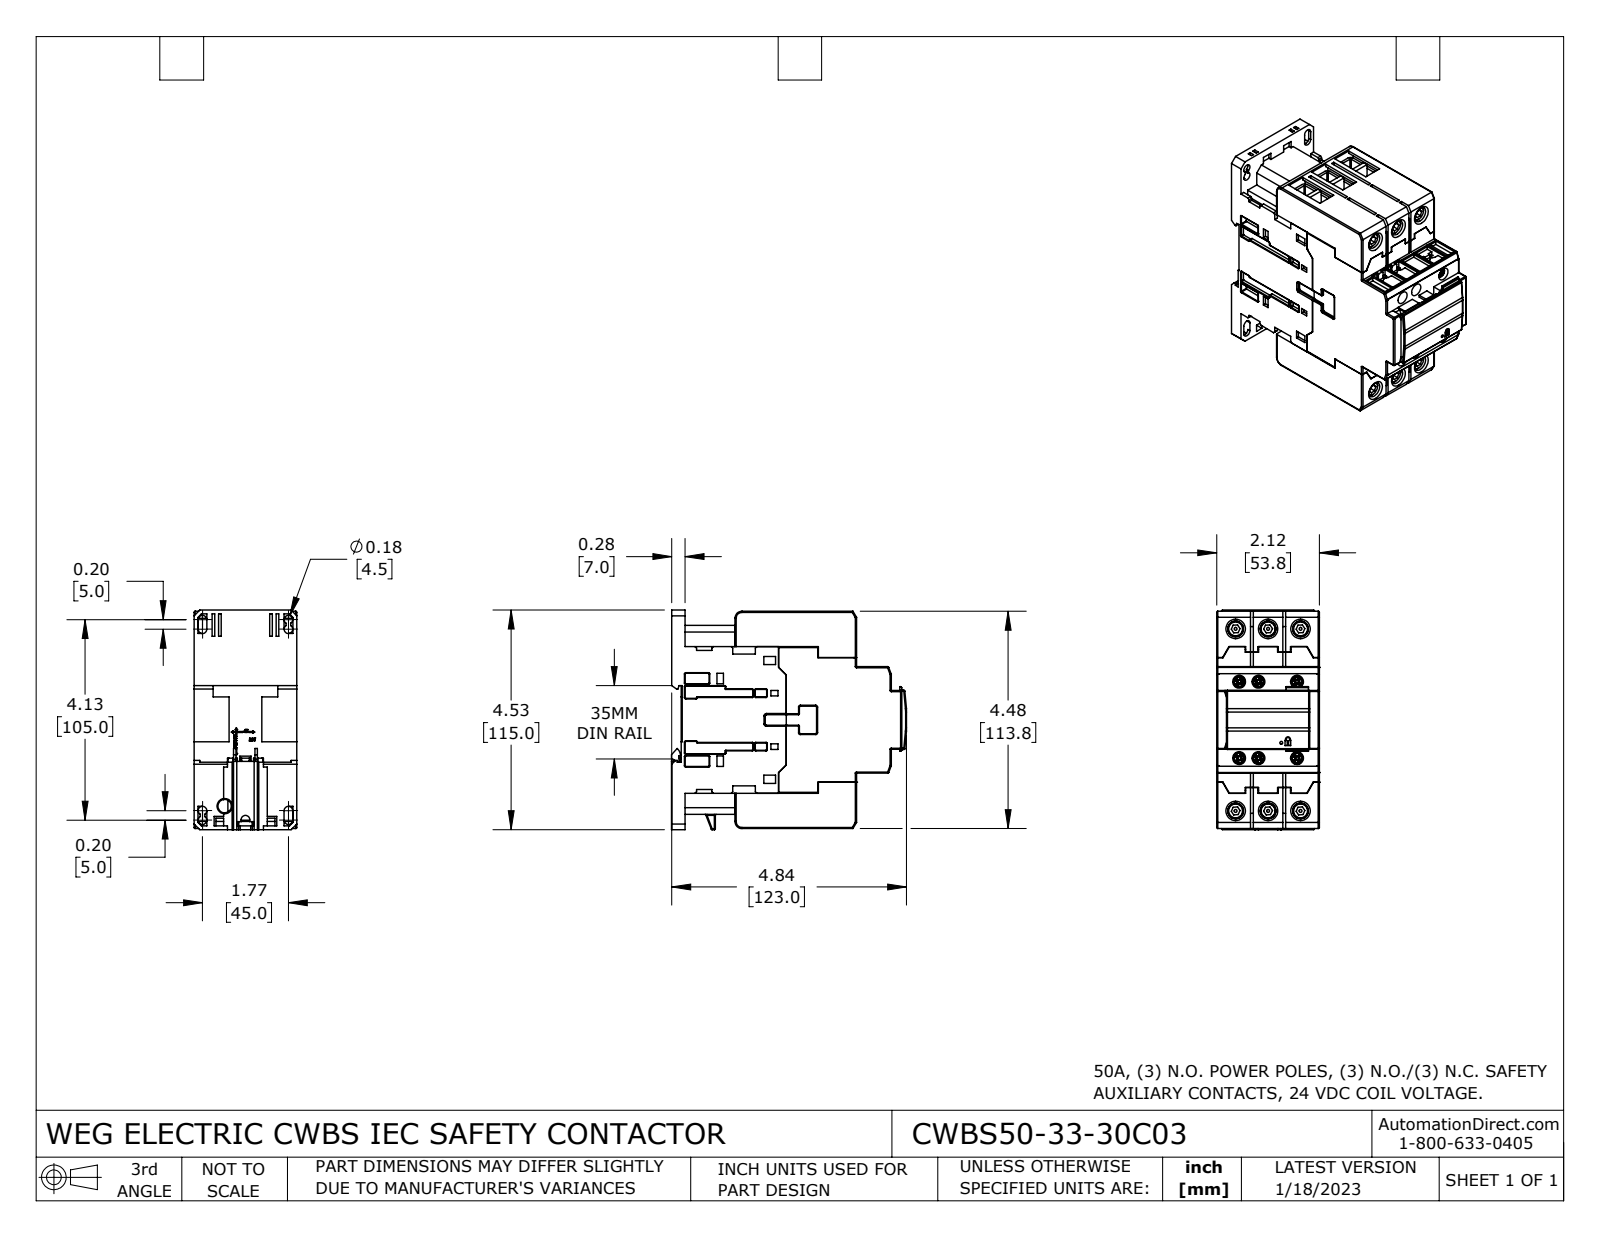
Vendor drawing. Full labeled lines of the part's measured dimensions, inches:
Part name (STEP PRODUCT): CWBS50-33-30C03
STEP written by: SolidWorks 2021 (CONFIG_CONTROL_DESIGN)
Units: inches
Bodies: 37 solids, 2637 faces (1669 planar, 550 cylindrical, 418 other)
Overall size (bounding box): 4.846 × 4.528 × 2.118
Volume: 33.67 in³ · Surface area: 209.3 in²
Round holes (diameter × count): ⌀0.124 ×6, ⌀0.197 ×6, ⌀0.264 ×6, ⌀0.323 ×6, ⌀0.177 ×4, ⌀0.125 ×2, ⌀0.276 ×2, ⌀0.059 ×1
Round bosses / shafts (diameter × count): ⌀0.343 ×6, ⌀0.236 ×6, ⌀0.135 ×6
Partial cylindrical surfaces — rounded edges, fillets, slot ends (radius × count): R0.02 ×89, R0.012 ×69, R0.004 ×48, R0.024 ×42, R0.079 ×18, R0.089 ×5, R0.039 ×3, R0.059 ×3
Main face-to-face distances: 0.059, 2.118, 0.669, 0.728, 3.024, 3.752, 0.108, 0.217, 3.811, 0.098
Hole centre spacings: 0.669, 1.091, 1.241, 1.669, 2.665, 2.73, 2.949, 3.811
